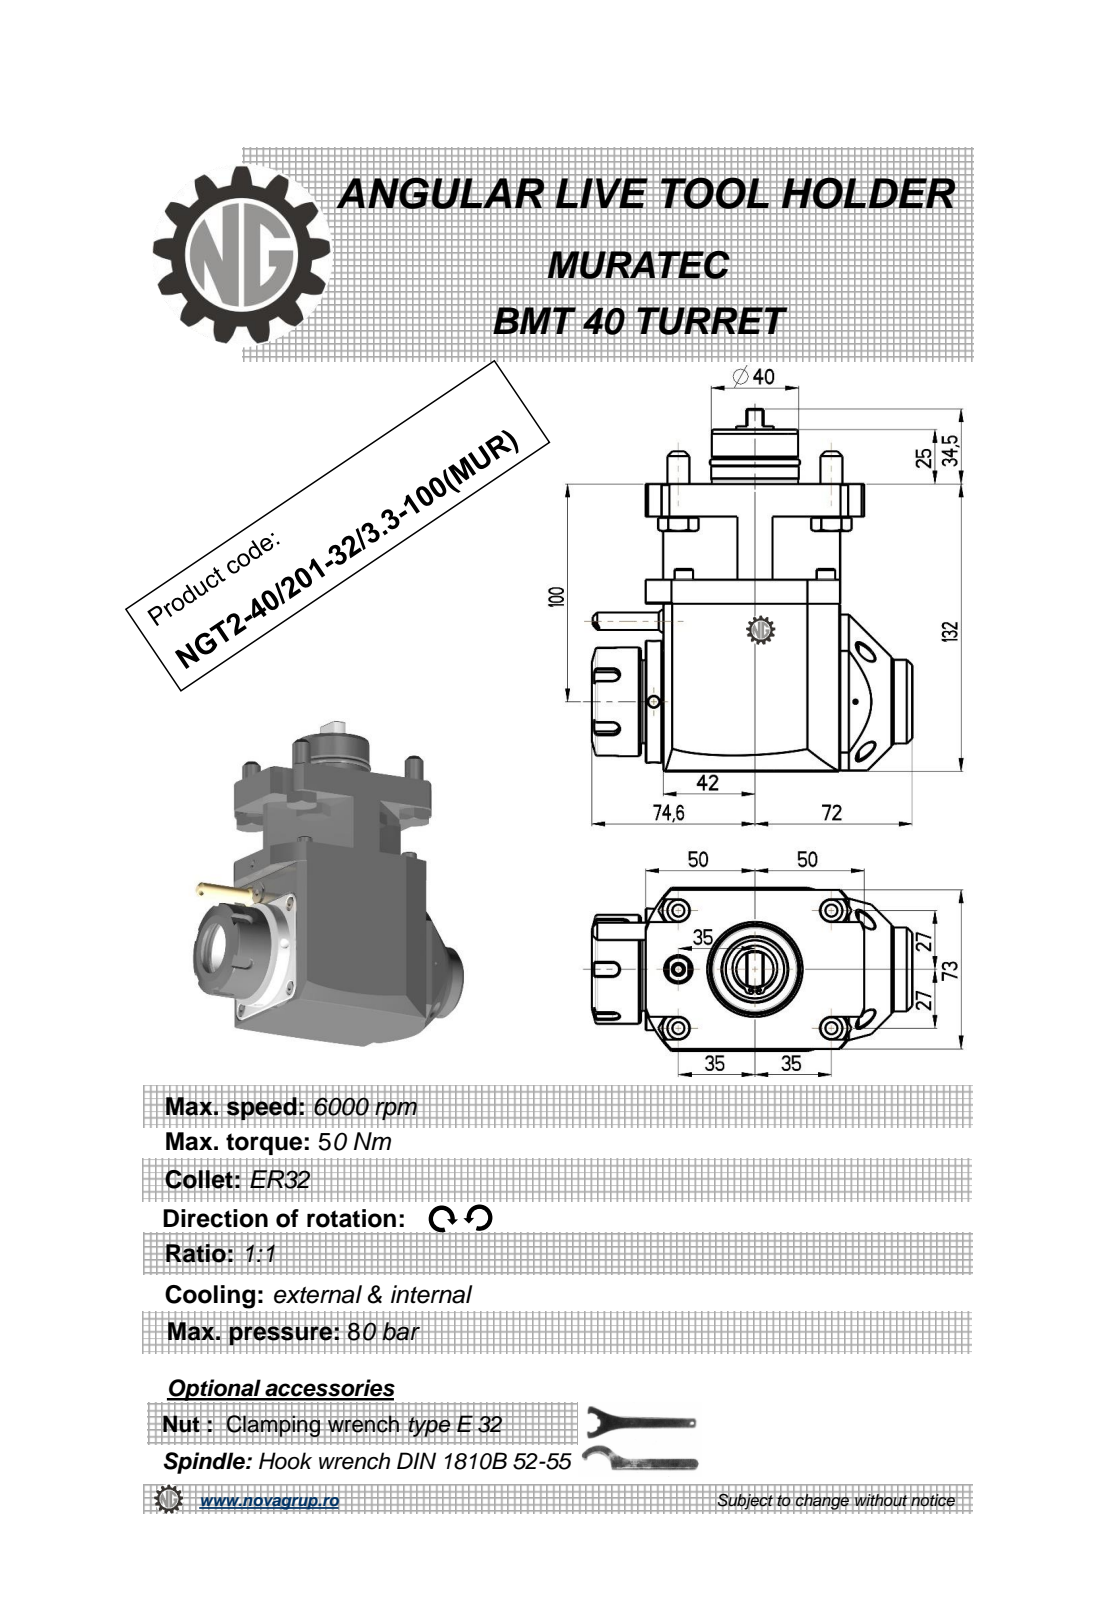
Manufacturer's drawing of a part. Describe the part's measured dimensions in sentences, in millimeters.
The part is named "NGT2_40_201_32_3_3_100_MUR". Its 3-D file was written by "PRO/ENGINEER BY PARAMETRIC TECHNOLOGY CORPORATION, 2010280 (CONFIG_CONTROL_DESIGN)". It is 2 solids with 416 faces: 177 planar, 86 cylindrical and 153 other. Overall it measures 166.5 by 146.6 by 75 millimeters. Its volume is 928 071 cubic millimeters and its surface area 83 093 square millimeters. Round holes: 3 of diameter 5, 1 of diameter 3, 1 of diameter 4.2, 1 of diameter 27. Round bosses or shafts: 4 of diameter 14.6, 4 of diameter 10, 1 of diameter 56, 1 of diameter 50, 1 of diameter 43, 1 of diameter 41, 1 of diameter 40, 1 of diameter 39.5. Partial cylindrical surfaces (rounded edges, fillets, slot ends): 6 of radius 0.22, 5 of radius 3, 4 of radius 5.25, 1 of radius 6, 1 of radius 40, 1 of radius 53.5. The main face-to-face distances are 132, 75, 1, 74, 44, 88, 63, 15, 29, 117. The hole center spacings are 11.25, 40.93.
